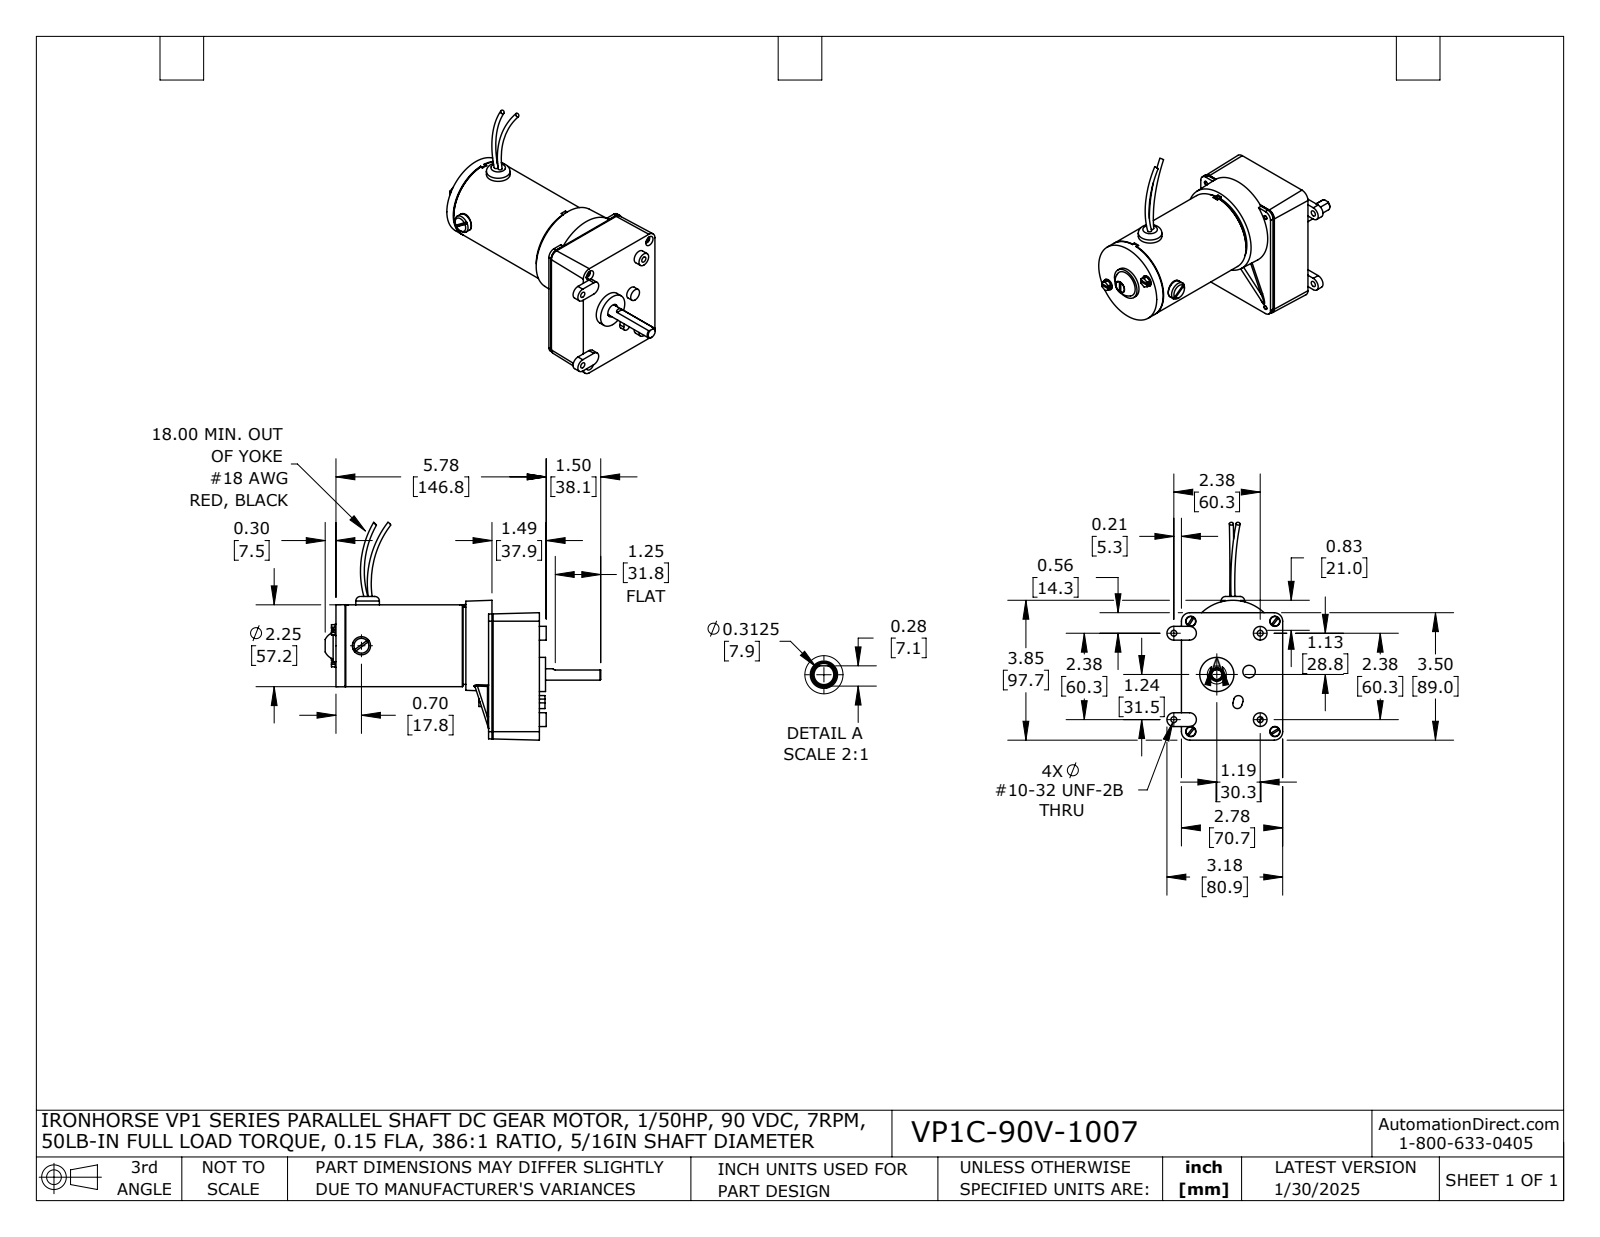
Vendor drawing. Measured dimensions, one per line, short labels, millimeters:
name: VP1C-90V-1007
written by: SolidWorks 2021 (AUTOMOTIVE_DESIGN)
unit: mm
bodies: 34 solids, 1338 faces (477 planar, 580 cylindrical, 281 other)
size: 192.5 × 152.1 × 80.8
volume: 224 700 mm³; area: 146 200 mm²
holes: 7× ⌀7.1, 4× ⌀0.9, 4× ⌀3, 4× ⌀3.8, 4× ⌀3.8, 4× ⌀4.1, 2× ⌀3.2, 2× ⌀4.7, 1× ⌀3.2, 1× ⌀3.2, 1× ⌀5.4, 1× ⌀6.1
bosses: 4× ⌀3.5, 3× ⌀8, 2× ⌀9.5, 1× ⌀57.3, 1× ⌀57.2, 1× ⌀53.9, 1× ⌀50.9, 1× ⌀50.8
rounds: 24× R0.7, 24× R1.3, 12× R0.5, 12× R1.4, 12× R1.5, 8× R0.8, 8× R0.8, 8× R4.8
face distances: 33.1, 2.5, 30.7, 35.5, 33, 2.4, 32.3, 29.9, 0.8, 3.1
hole spacings: 22.2, 19.6, 49.2, 58.7, 58.7, 77, 77, 3.4
